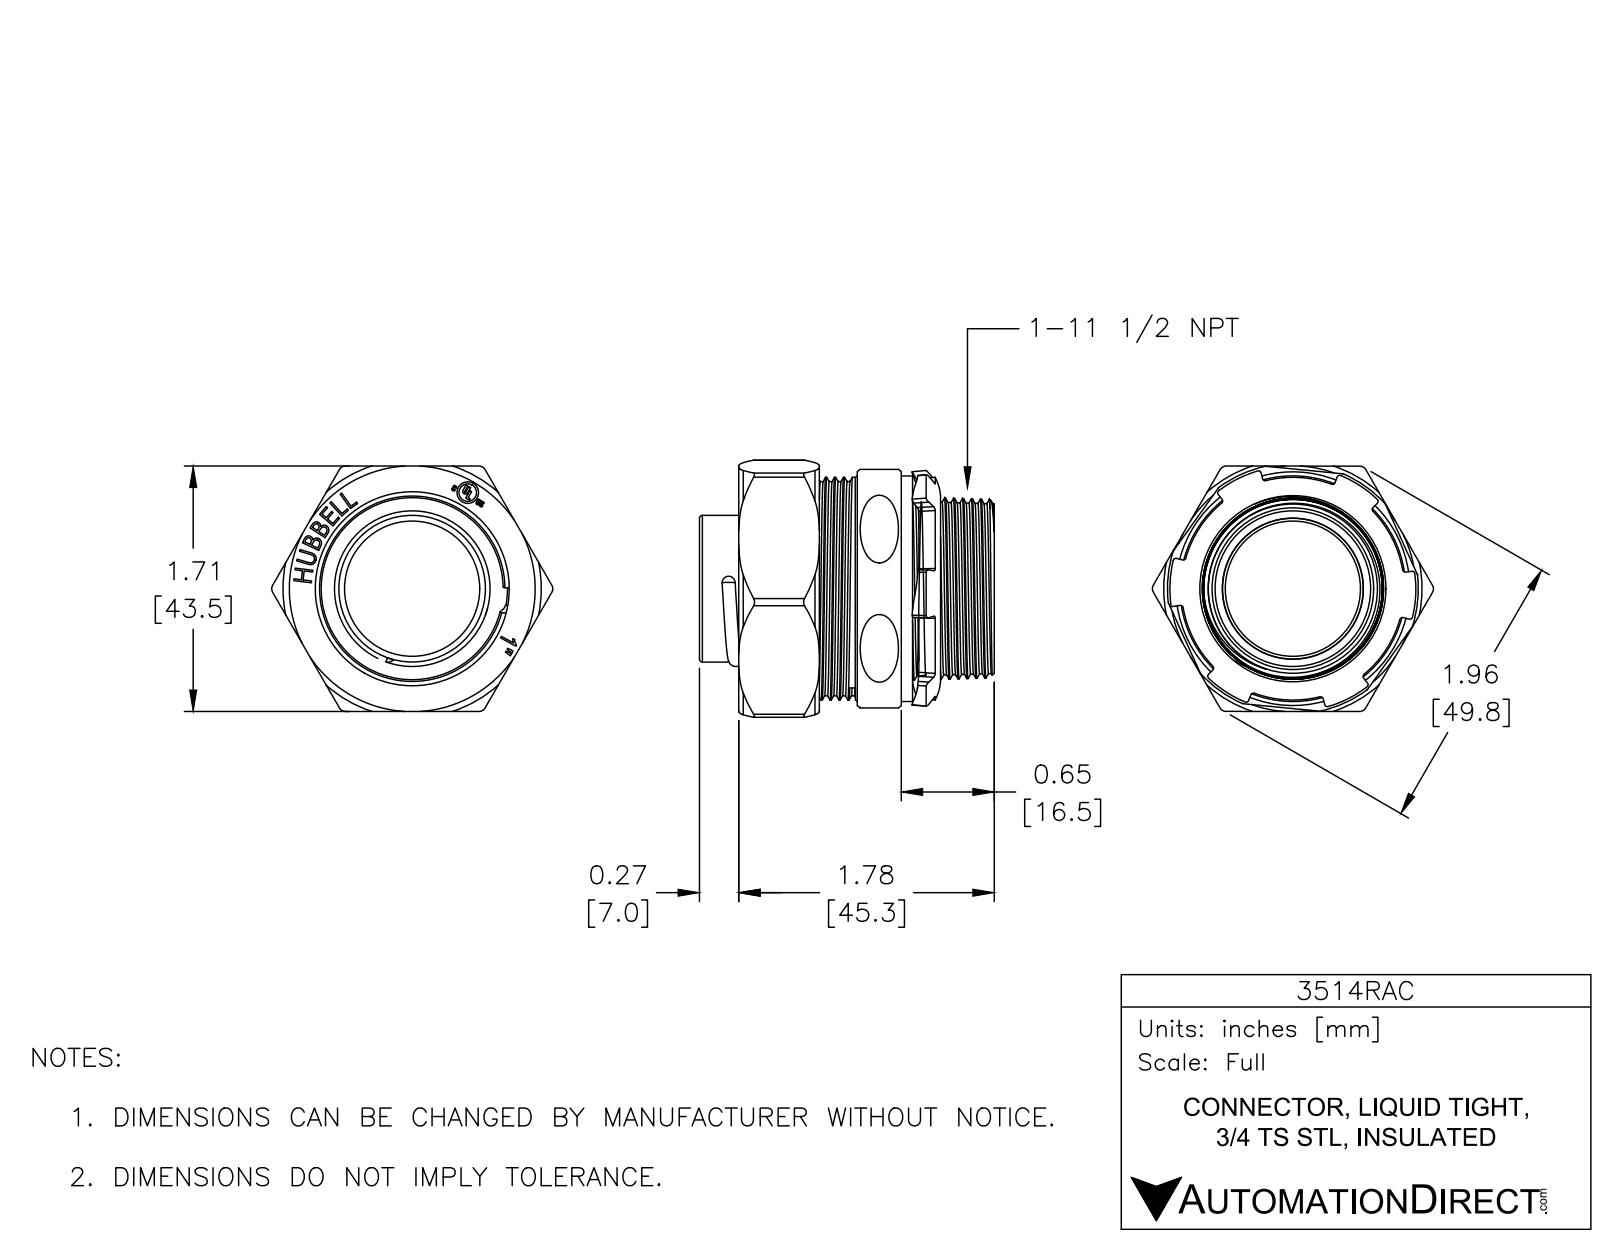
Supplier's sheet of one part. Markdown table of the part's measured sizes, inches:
| quantity | value |
| --- | --- |
| part name | 3514RAC; 3514RAC-4; 3514RAC-1; 3514RAC-2 (+4 more) |
| STEP written by | SolidWorks 2017 (AUTOMOTIVE_DESIGN) |
| units | inches |
| bodies | 7 solids, 502 faces (186 planar, 99 cylindrical, 217 other) |
| overall size | 2.117 × 1.954 × 1.795 |
| volume | 1.148 in³ |
| surface area | 49.24 in² |
| round holes (diameter × count) | 0.15 × 1, 0.943 × 1, 0.985 × 1, 1.215 × 1, 1.331 × 1, 1.335 × 1, 1.354 × 1, 1.395 × 1, 1.516 × 1 |
| round bosses / shafts (diameter × count) | 1.575 × 1, 1.555 × 1, 1.496 × 1, 1.37 × 1, 1.161 × 1, 1.024 × 1, 0.983 × 1, 0.122 × 1 |
| partial cylindrical surfaces (radius × count) | 0.01 × 8, 0.05 × 6, 0.046 × 2, 0.005 × 1, 0.013 × 1, 0.019 × 1 |
| main face-to-face distances | 1.135, 1.214, 0.079, 0.08, 1.055, 0.159, 1.713, 1.713, 1.712, 1.665 |
| hole center spacings | 0.775 |
